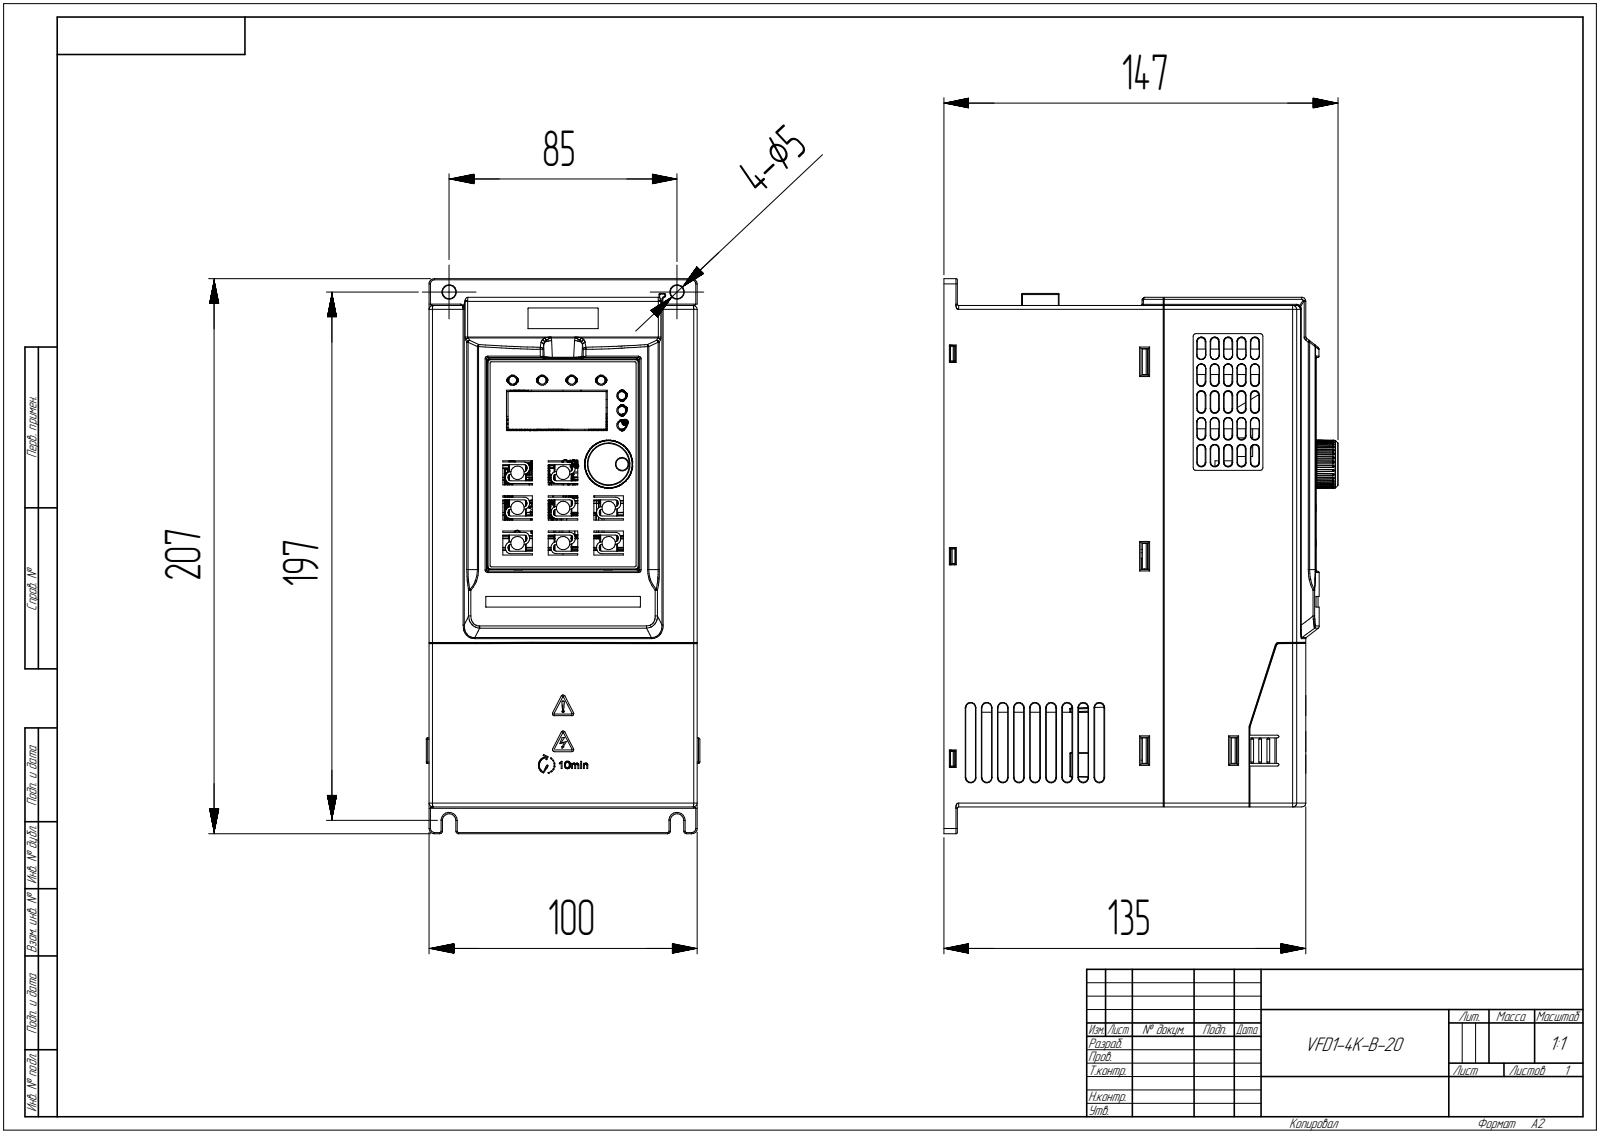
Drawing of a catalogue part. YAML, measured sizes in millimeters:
part_name: "PRT0001"
step_written_by: "CREO PARAMETRIC BY PTC INC, 2020074 (CONFIG_CONTROL_DESIGN)"
units: millimeters
bodies: {solids: 1, faces: 8245, planar: 4745, cylindrical: 1950, other: 1550}
overall_size: [207, 147, 102]
volume: 2270000
surface_area: 493295
round_holes:
  - {diameter: 2, count: 8}
  - {diameter: 2.5, count: 7}
  - {diameter: 3.8, count: 7}
  - {diameter: 1.5, count: 6}
  - {diameter: 1.8, count: 6}
  - {diameter: 3, count: 5}
  - {diameter: 3.5, count: 3}
  - {diameter: 7.5, count: 3}
  - {diameter: 1, count: 2}
  - {diameter: 5, count: 2}
  - {diameter: 2.7, count: 1}
  - {diameter: 7.2, count: 1}
round_bosses_or_shafts:
  - {diameter: 5.4, count: 8}
  - {diameter: 5, count: 8}
  - {diameter: 3.5, count: 8}
  - {diameter: 3, count: 8}
  - {diameter: 4, count: 6}
  - {diameter: 6, count: 4}
  - {diameter: 9.5, count: 3}
  - {diameter: 1.8, count: 2}
partial_cylinders:
  - {radius: 0.5, count: 434}
  - {radius: 0.3, count: 226}
  - {radius: 1, count: 153}
  - {radius: 0.2, count: 68}
  - {radius: 2, count: 53}
  - {radius: 0.34, count: 35}
  - {radius: 2.7, count: 23}
  - {radius: 1.5, count: 16}
face_to_face_distances: [1.29, 98.71, 2.2, 1.5, 97.42, 100, 117.4, 0.72, 4, 1.8]
hole_center_spacings: [47.14, 50, 61.4, 72.4, 94.93, 47.79, 85, 98.49]
